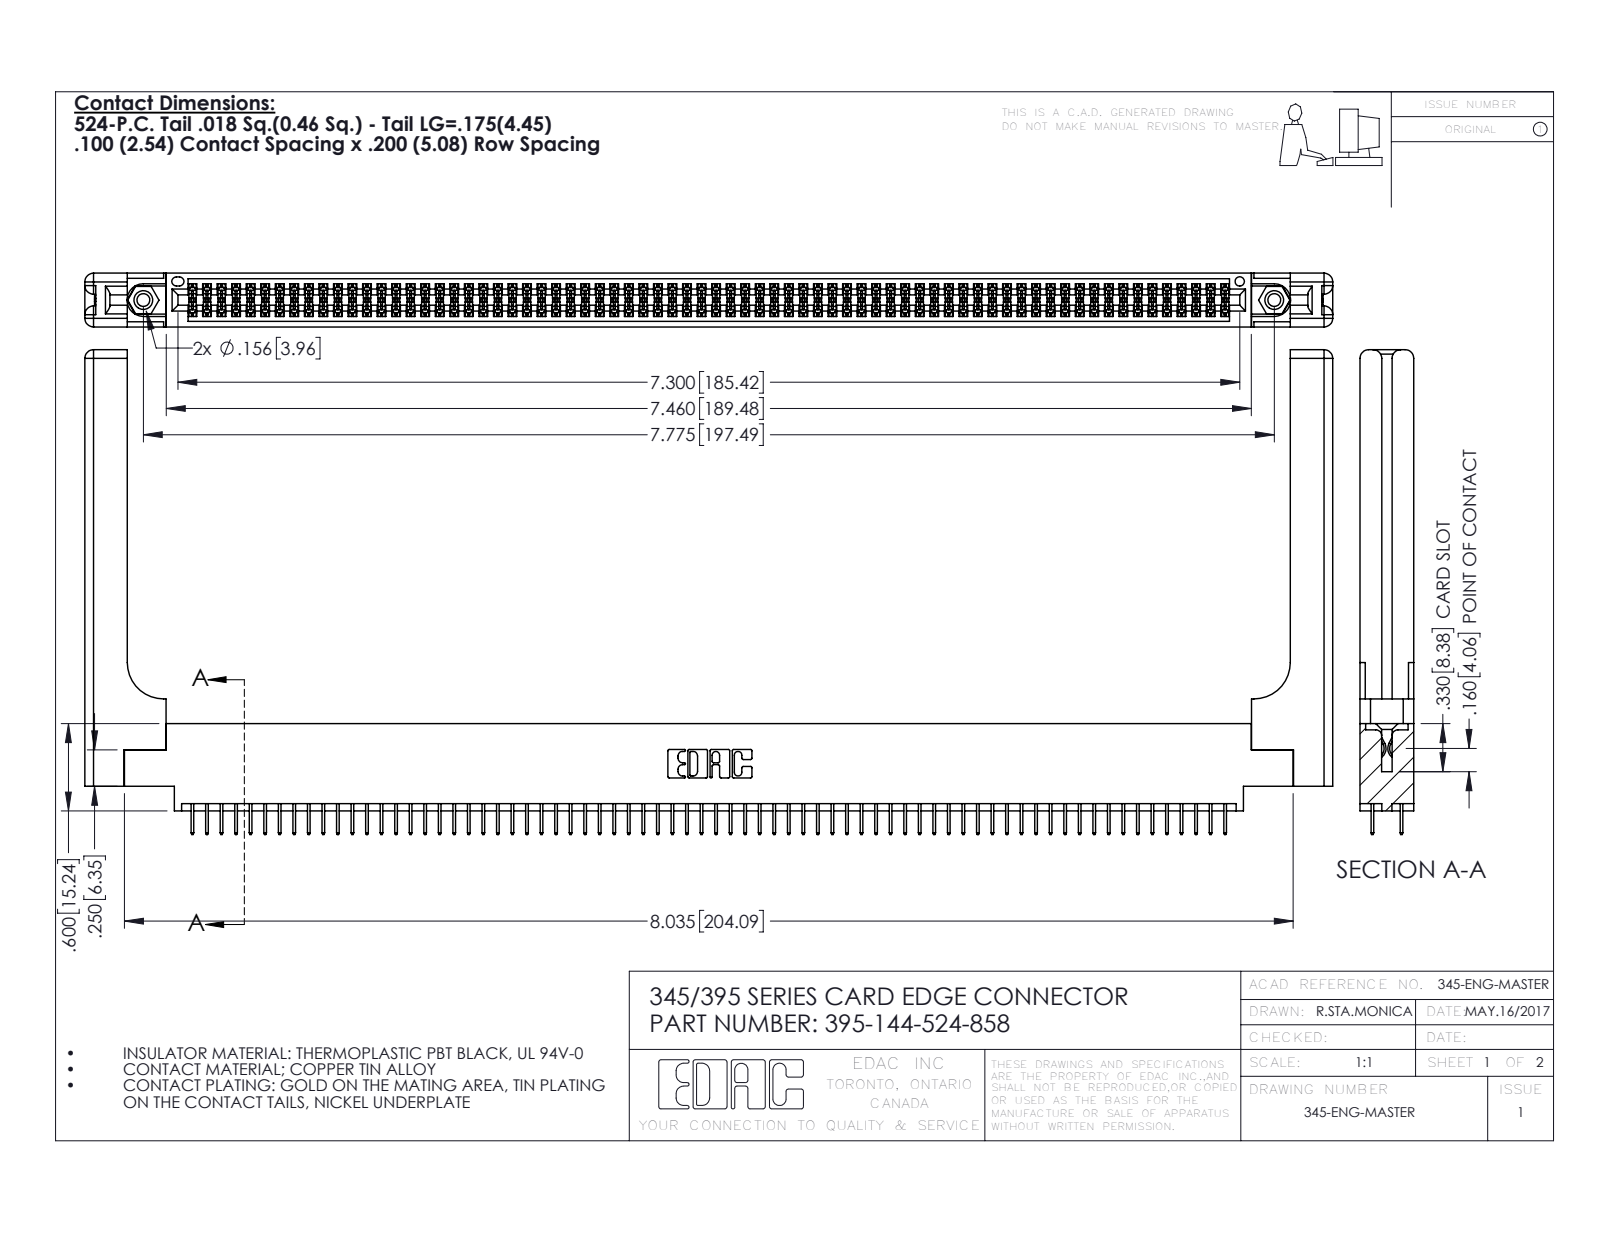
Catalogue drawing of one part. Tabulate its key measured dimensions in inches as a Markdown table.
| quantity | value |
| --- | --- |
| part name | 345-250-001_345-250-001-102; 395-144-524-858; 345-220-058_345-220-058; 345 Part_0.170 Offset - 0.156 Dia-TH (+1 more) |
| STEP written by | SolidWorks 2016 (CONFIG_CONTROL_DESIGN) |
| units | inches |
| bodies | 149 solids, 8162 faces (5848 planar, 2254 cylindrical, 60 other) |
| overall size | 8.579 × 3.332 × 0.37 |
| volume | 1.806 in³ |
| surface area | 56.45 in² |
| round holes (diameter × count) | 0.089 × 2, 0.125 × 2, 0.156 × 2, 0.064 × 1 |
| round bosses / shafts (diameter × count) | 0.155 × 2 |
| partial cylindrical surfaces (radius × count) | 0.006 × 216, 0.01 × 22, 0.06 × 16, 0.007 × 6, 0.031 × 6, 0.026 × 3, 0.014 × 2, 0.019 × 2 |
| main face-to-face distances | 0.072, 0.298, 0.37, 0.2, 0.098, 0.272, 0.025, 0.225, 0.175, 0.072 |
| hole center spacings | 0.27, 7.539, 7.775 |
